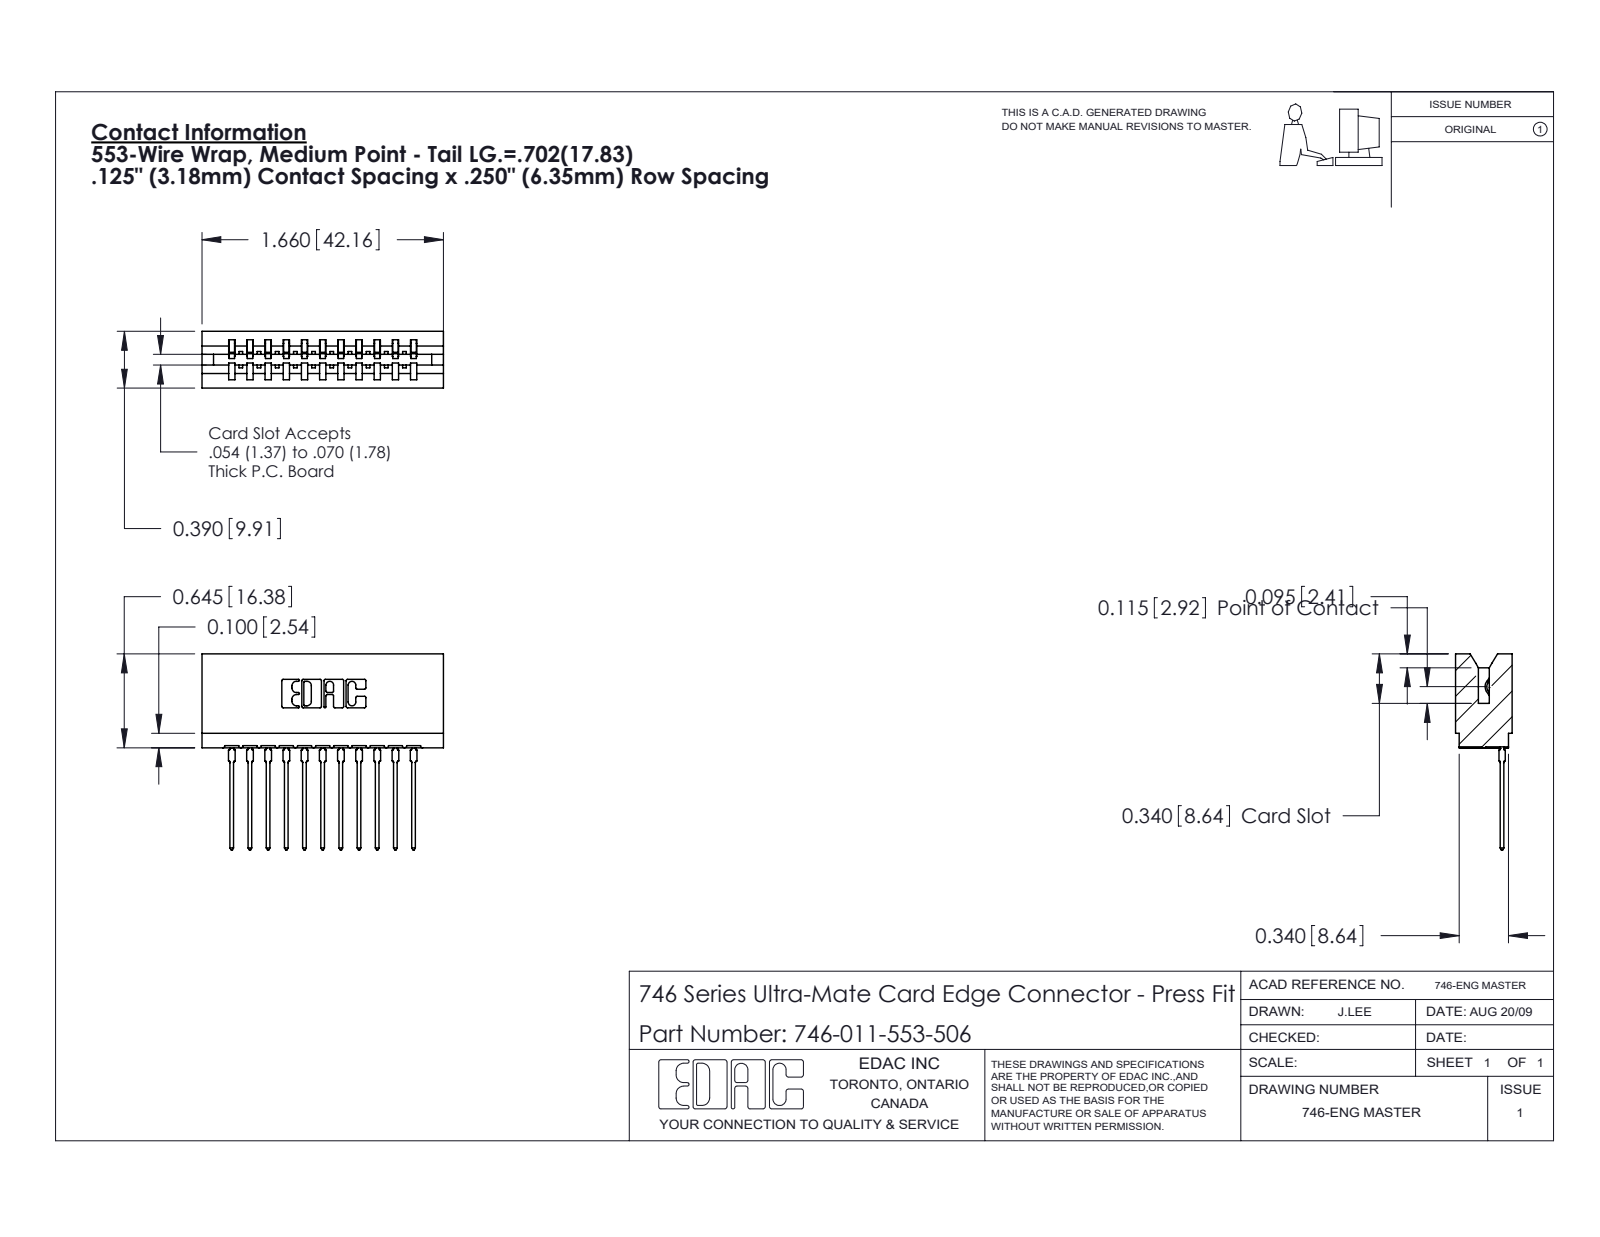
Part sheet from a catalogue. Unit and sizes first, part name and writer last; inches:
Units: inches
Overall size (bounding box): 1.66 × 1.346 × 0.39
Partial cylindrical surfaces — rounded edges, fillets, slot ends (radius × count): R0.01 ×22, R0.021 ×22, R0.015 ×12, R0.007 ×6, R0.031 ×6, R0.005 ×4, R0.011 ×4, R0.026 ×3
Main face-to-face distances: 0.25, 0.333, 0.5, 0.057, 0.125, 0.042, 0.125, 0.292, 0.542, 0.39
Volume: 0.302 in³ · Surface area: 9.938 in²
Bodies: 12 solids, 1286 faces (749 planar, 251 cylindrical, 286 other)
Part name (STEP PRODUCT): 746-292-001_553; 746 Part_.340 Slot Depth - 06; 746-011-553-506
STEP written by: SolidWorks 2020 (CONFIG_CONTROL_DESIGN)
